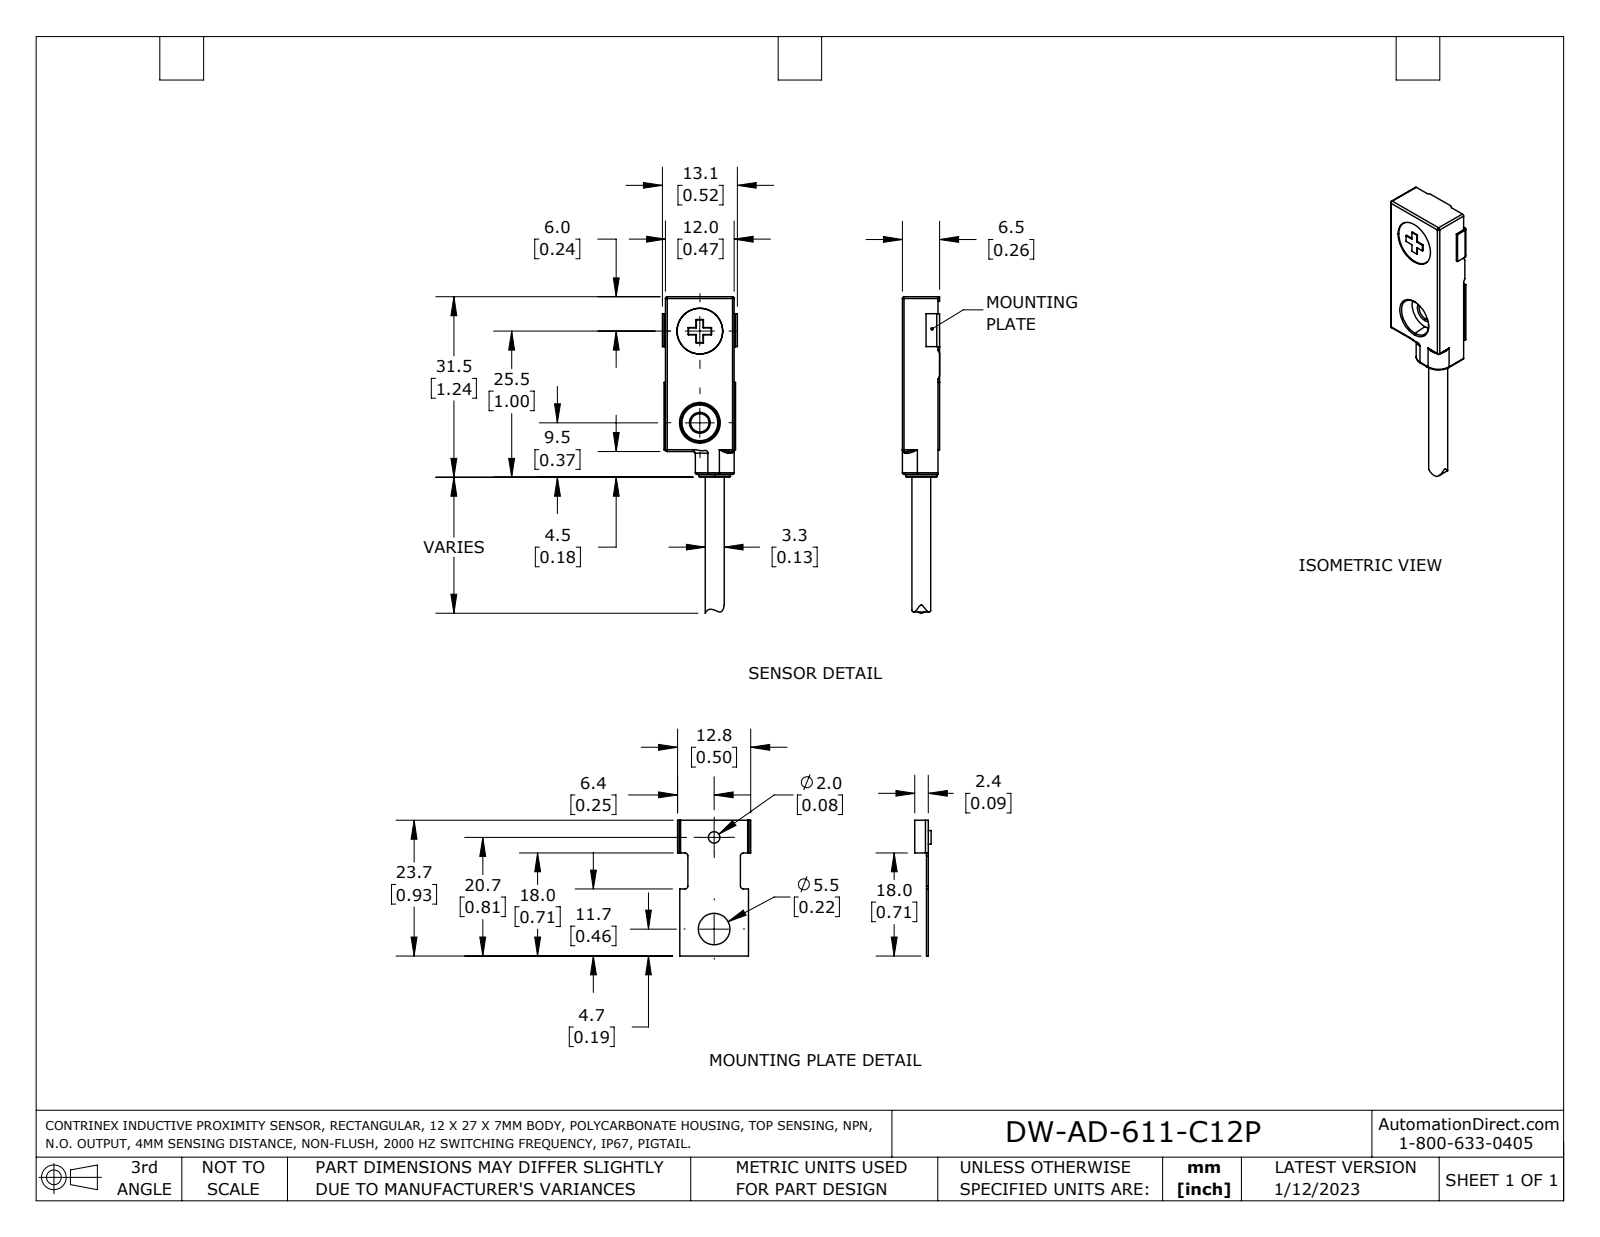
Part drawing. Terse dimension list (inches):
name: DW-AD-61X-C12P
written by: SolidWorks 2021 (AUTOMOTIVE_DESIGN)
unit: in
bodies: 2 solids, 112 faces (56 planar, 31 cylindrical, 25 other)
size: 2.174 × 0.516 × 0.256
volume: 0.143 in³; area: 3.307 in²
holes: 1× ⌀0.081, 1× ⌀0.126, 1× ⌀0.217
bosses: 2× ⌀0.217, 1× ⌀0.13
rounds: 12× R0.012, 6× R0.005, 2× R0.02, 1× R0.087, 1× R0.102
face distances: 0.244, 0.256, 0.472, 0.238, 0.25, 0.482, 1.063, 0.012, 0.022, 0.494
hole spacings: 0.629
